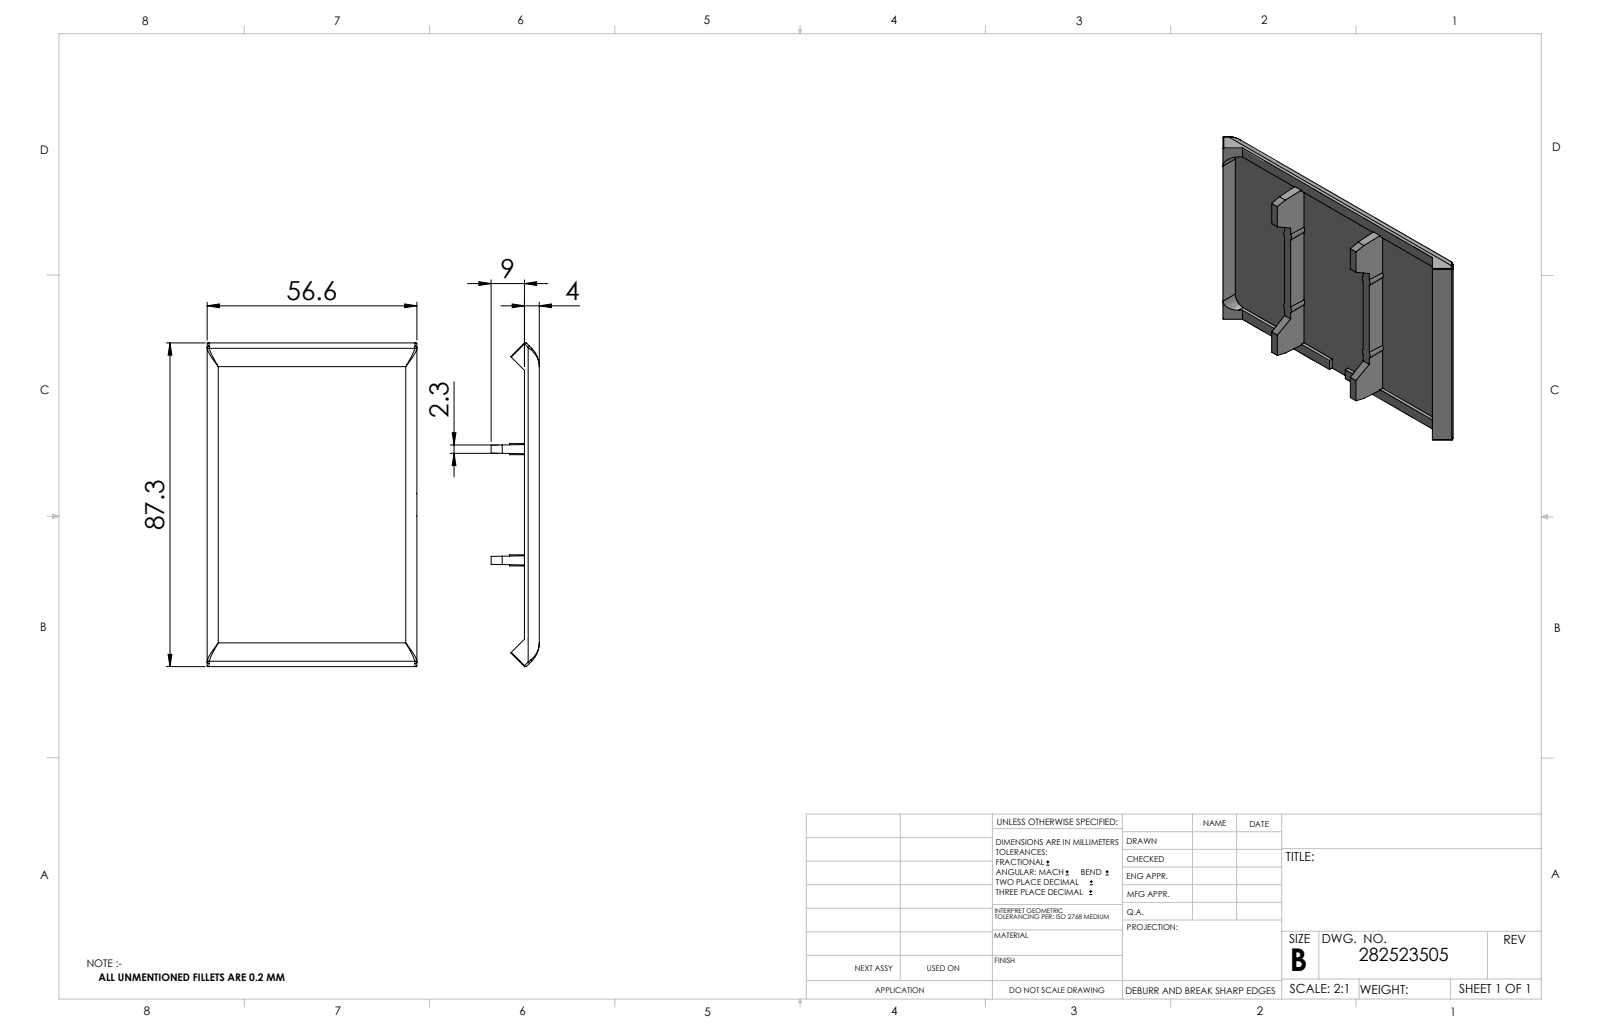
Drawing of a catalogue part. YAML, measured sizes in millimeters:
part_name: "282523505_c_1"
step_written_by: "SolidWorks 2014 (CONFIG_CONTROL_DESIGN)"
units: millimeters
bodies: {solids: 1, faces: 97, planar: 61, cylindrical: 28, other: 8}
overall_size: [87.3, 56.6, 13]
volume: 17099
surface_area: 12839
partial_cylinders:
  - {radius: 3, count: 6}
  - {radius: 0.2, count: 4}
  - {radius: 0.5, count: 4}
  - {radius: 1.5, count: 4}
  - {radius: 7, count: 2}
face_to_face_distances: [3, 30, 4, 1, 62.07, 79.9, 5, 8, 53.6, 56.6]
